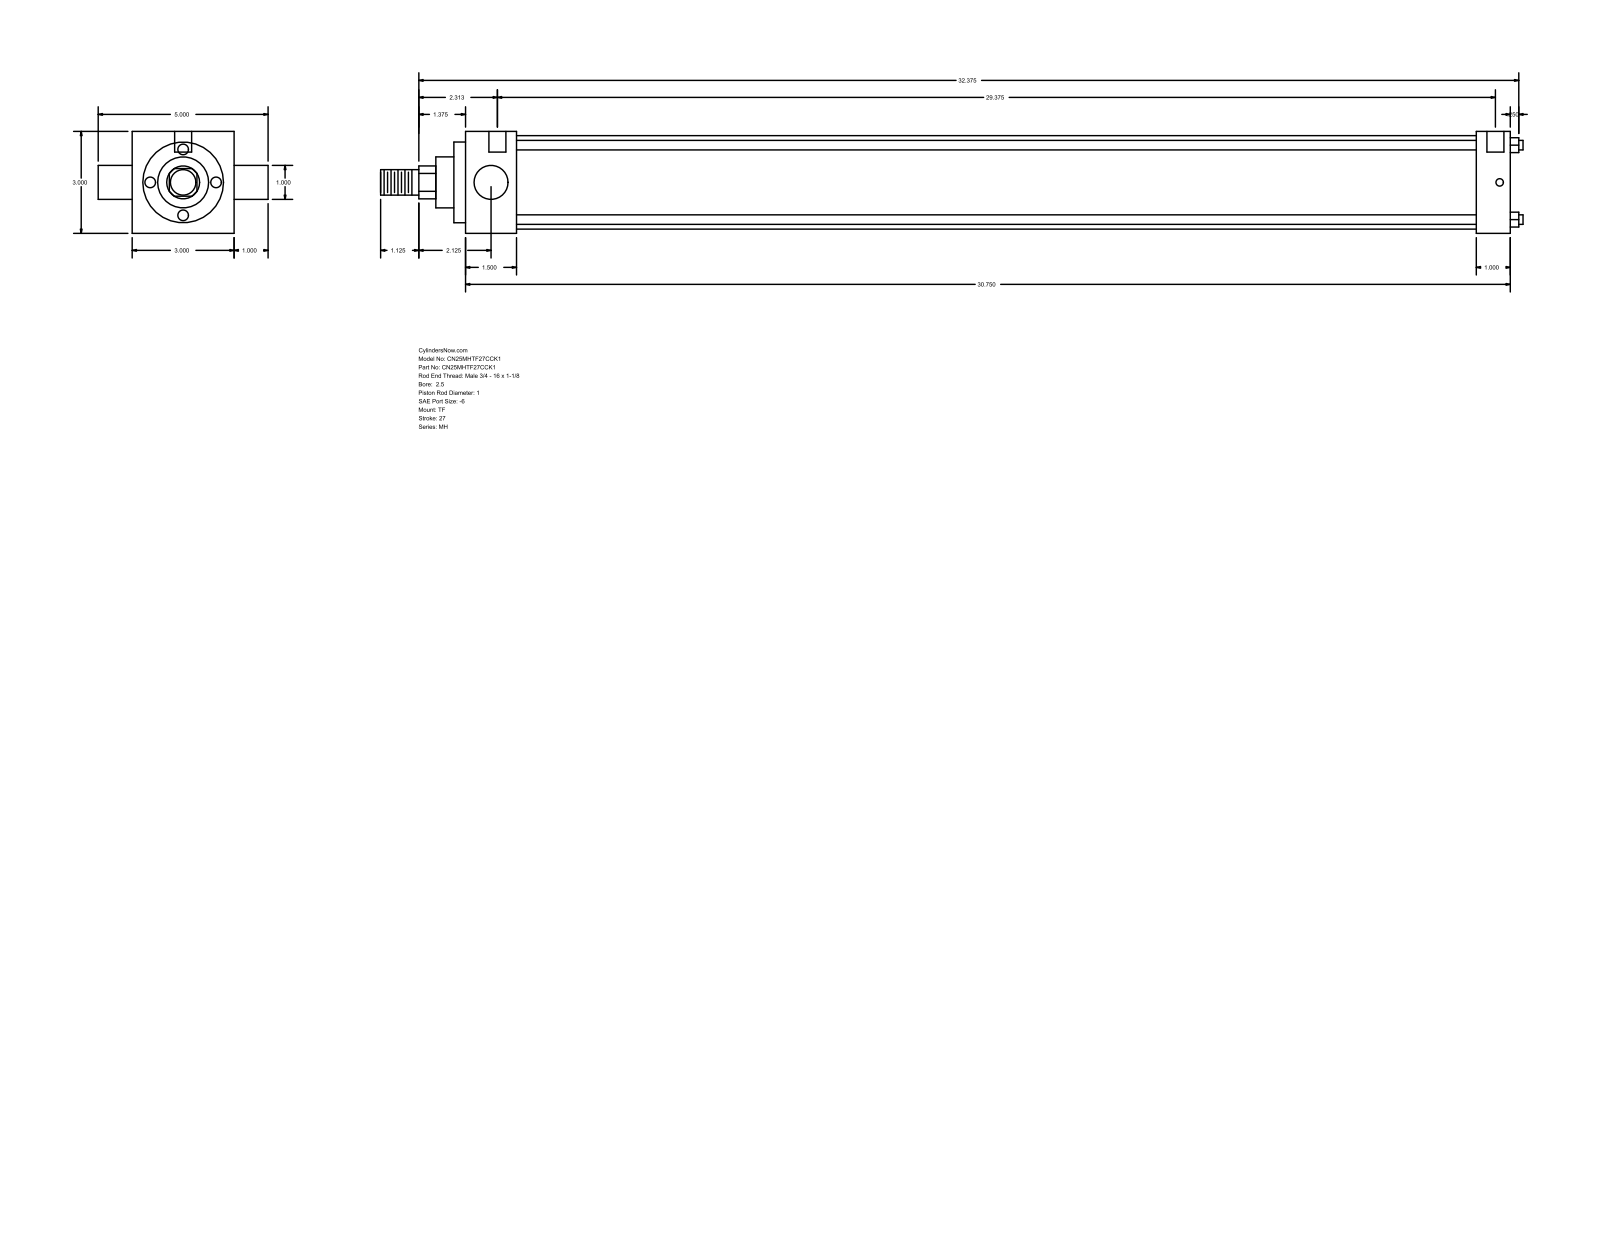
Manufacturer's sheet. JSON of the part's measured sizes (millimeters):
{"part_name": "MH_TF__0250_1", "step_written_by": "GSSL Pune (CONFIG_CONTROL_DESIGN)", "units": "millimeters", "bodies": {"solids": 0, "faces": 86, "planar": 61, "cylindrical": 25, "other": 0}, "overall_size": [854.08, 127, 76.2], "round_holes": [[5.56, 3], [12.7, 2]], "round_bosses_or_shafts": [[7.14, 4], [25.4, 2], [69.85, 1], [60.33, 1], [38.1, 1], [19.05, 1]], "partial_cylinders_radius": [[12.29, 1]], "face_to_face_distances": [76.2, 781.06, 25.4, 38.11, 742.95, 755.66, 717.55, 8.73, 46.84, 764.39], "hole_center_spacings": [3.18, 4.76, 746.12, 749.3, 750.88, 754.06]}
